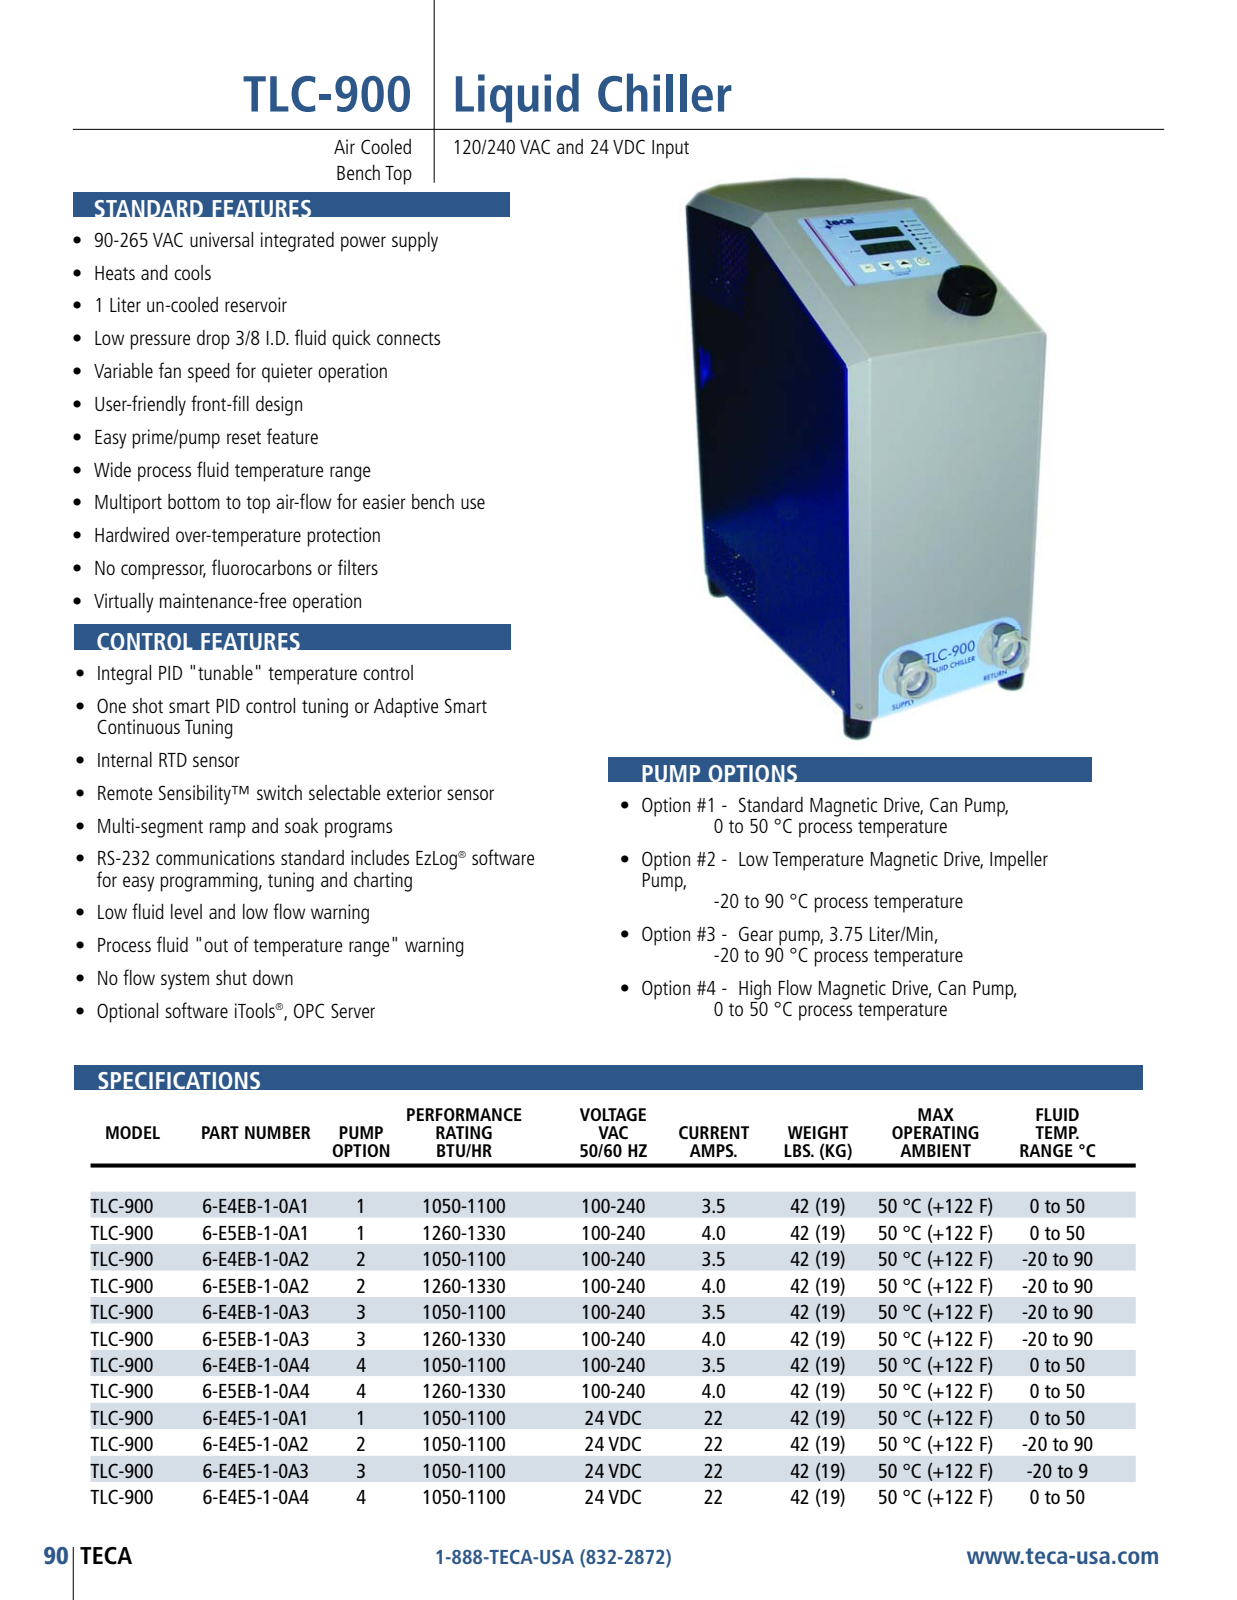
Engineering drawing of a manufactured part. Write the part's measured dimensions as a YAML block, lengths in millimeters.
part_name: "TLC-900"
step_written_by: "SolidWorks 2016 (CONFIG_CONTROL_DESIGN)"
units: millimeters
bodies: {solids: 0, faces: 18752, planar: 16124, cylindrical: 1366, other: 1262}
overall_size: [471.1, 422.6, 195.9]
round_holes:
  - {diameter: 6, count: 6}
  - {diameter: 2.7, count: 5}
  - {diameter: 5, count: 5}
  - {diameter: 3.5, count: 4}
  - {diameter: 3.5, count: 4}
  - {diameter: 3.8, count: 4}
  - {diameter: 9.5, count: 4}
  - {diameter: 4.7, count: 3}
  - {diameter: 2.6, count: 2}
  - {diameter: 10.9, count: 2}
  - {diameter: 11.7, count: 2}
  - {diameter: 12.2, count: 2}
round_bosses_or_shafts:
  - {diameter: 6.9, count: 17}
  - {diameter: 6.4, count: 15}
  - {diameter: 6.2, count: 15}
  - {diameter: 3.4, count: 14}
  - {diameter: 6, count: 11}
  - {diameter: 3.5, count: 9}
  - {diameter: 8, count: 8}
  - {diameter: 15.9, count: 5}
partial_cylinders:
  - {radius: 0.6, count: 65}
  - {radius: 0.7, count: 56}
  - {radius: 1.2, count: 55}
  - {radius: 0.3, count: 26}
  - {radius: 0.8, count: 25}
  - {radius: 1.5, count: 25}
  - {radius: 0.6, count: 22}
  - {radius: 0.5, count: 15}
face_to_face_distances: [3.8, 7.6, 11.4, 15.2, 19.1, 1.3, 22.9, 1.2, 38.1, 34.3]
hole_center_spacings: [14, 33, 47, 19.1, 27.9, 61, 45.8, 10.7]
